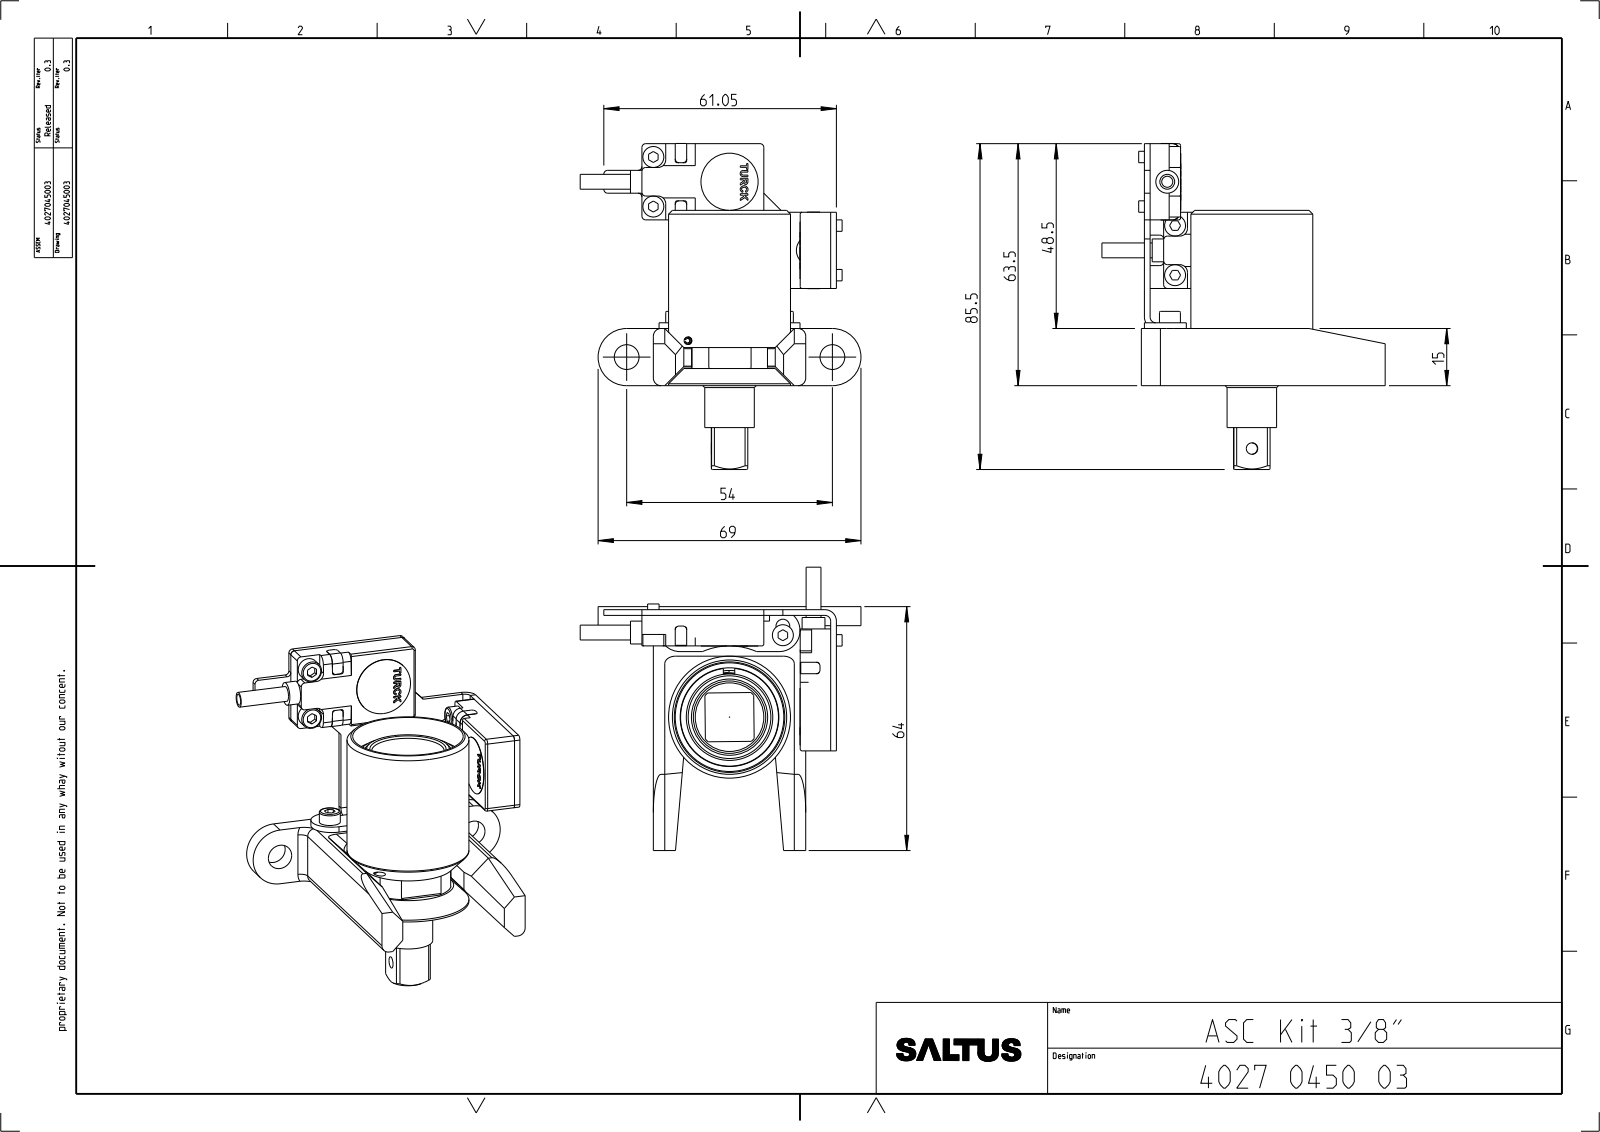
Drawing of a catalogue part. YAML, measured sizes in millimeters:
part_name: "4027045160; 4027045150; 4027045161; 0211110500 (+8 more)"
step_written_by: "CREO PARAMETRIC BY PTC INC, 2022414 (CONFIG_CONTROL_DESIGN)"
units: millimeters
bodies: {solids: 19, faces: 749, planar: 351, cylindrical: 245, other: 153}
overall_size: [85.55, 74.35, 73.7]
volume: 56312
surface_area: 37621
round_holes:
  - {diameter: 3, count: 7}
  - {diameter: 2.5, count: 6}
  - {diameter: 3.4, count: 4}
  - {diameter: 2.9, count: 2}
  - {diameter: 6.1, count: 2}
  - {diameter: 6.5, count: 2}
  - {diameter: 1.2, count: 1}
  - {diameter: 2, count: 1}
  - {diameter: 5.5, count: 1}
  - {diameter: 18, count: 1}
  - {diameter: 19, count: 1}
  - {diameter: 22.85, count: 1}
round_bosses_or_shafts:
  - {diameter: 5.5, count: 6}
  - {diameter: 15, count: 2}
  - {diameter: 6, count: 2}
  - {diameter: 3.9, count: 2}
  - {diameter: 32, count: 1}
  - {diameter: 28.5, count: 1}
  - {diameter: 22.7, count: 1}
  - {diameter: 13, count: 1}
partial_cylinders:
  - {radius: 1, count: 30}
  - {radius: 0.5, count: 21}
  - {radius: 2, count: 19}
  - {radius: 0.3, count: 8}
  - {radius: 1.8, count: 4}
  - {radius: 2.05, count: 4}
  - {radius: 1.5, count: 2}
  - {radius: 3, count: 2}
face_to_face_distances: [1.5, 15, 2.3, 0.8, 8.05, 9.5, 8, 3, 40, 5]
hole_center_spacings: [13, 28.22, 33, 11.68, 24.59, 28, 28.43, 40.12]
